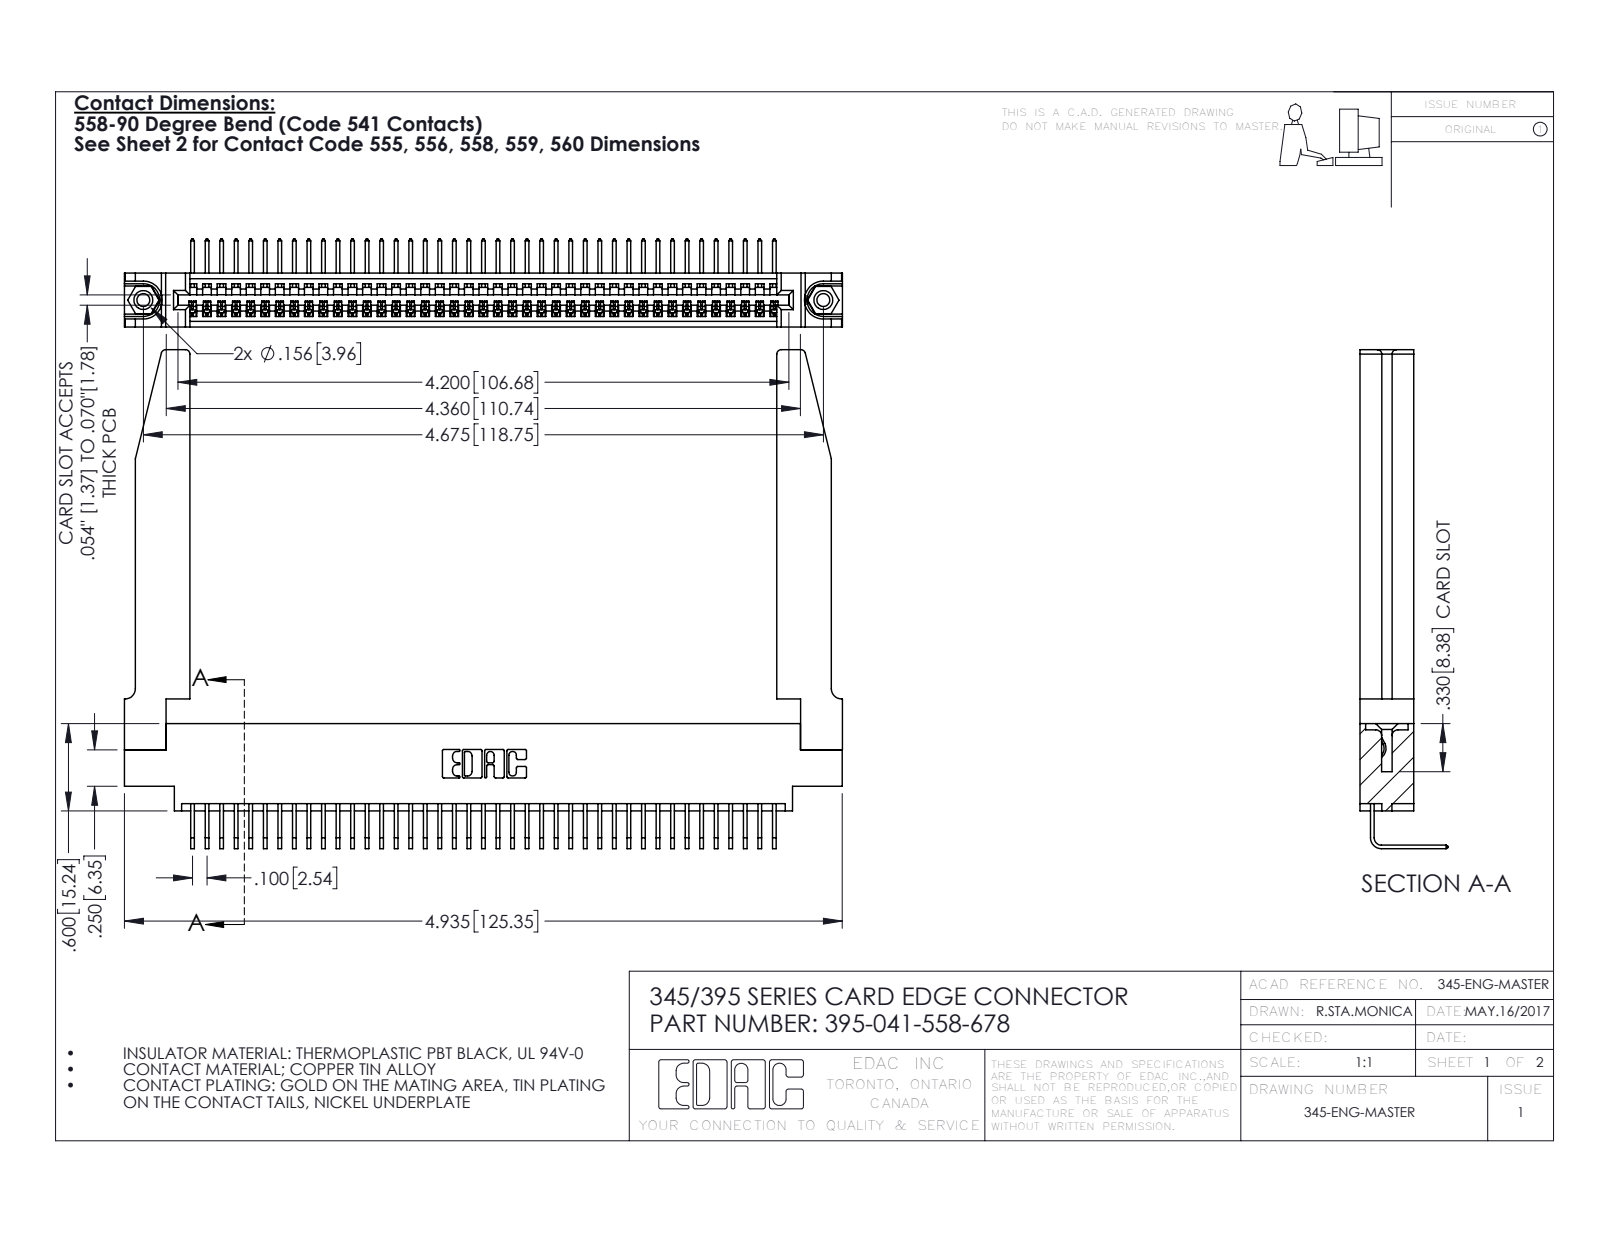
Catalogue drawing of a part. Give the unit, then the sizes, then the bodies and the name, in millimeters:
Units: millimetres
Overall size (bounding box): 125.4 × 87.1 × 15.4
Round holes (diameter × count): ⌀2.3 ×2, ⌀3.2 ×2, ⌀4 ×2, ⌀1.6 ×1
Round bosses / shafts (diameter × count): ⌀3.9 ×2
Partial cylindrical surfaces — rounded edges, fillets, slot ends (radius × count): R0.2 ×82, R0.3 ×22, R0.8 ×8, R0.2 ×6, R0.8 ×6, R0.7 ×3, R0.8 ×2, R1 ×2
Main face-to-face distances: 9.4, 1.8, 7.6, 5.1, 2.5, 6.9, 0.6, 5.7, 3.8, 3.8
Hole centre spacings: 6.9, 112.8, 118.7
Volume: 19 700 mm³ · Surface area: 23 610 mm²
Bodies: 46 solids, 2824 faces (1948 planar, 824 cylindrical, 52 other)
Part name (STEP PRODUCT): 345-220-078_345-220-078; 345 Part_0.170 Offset - 0.156 Dia-TH; 345-292-001_558 Tail - 2; 345-250-001_345-250-001-102 (+1 more)
STEP written by: SolidWorks 2016 (CONFIG_CONTROL_DESIGN)
